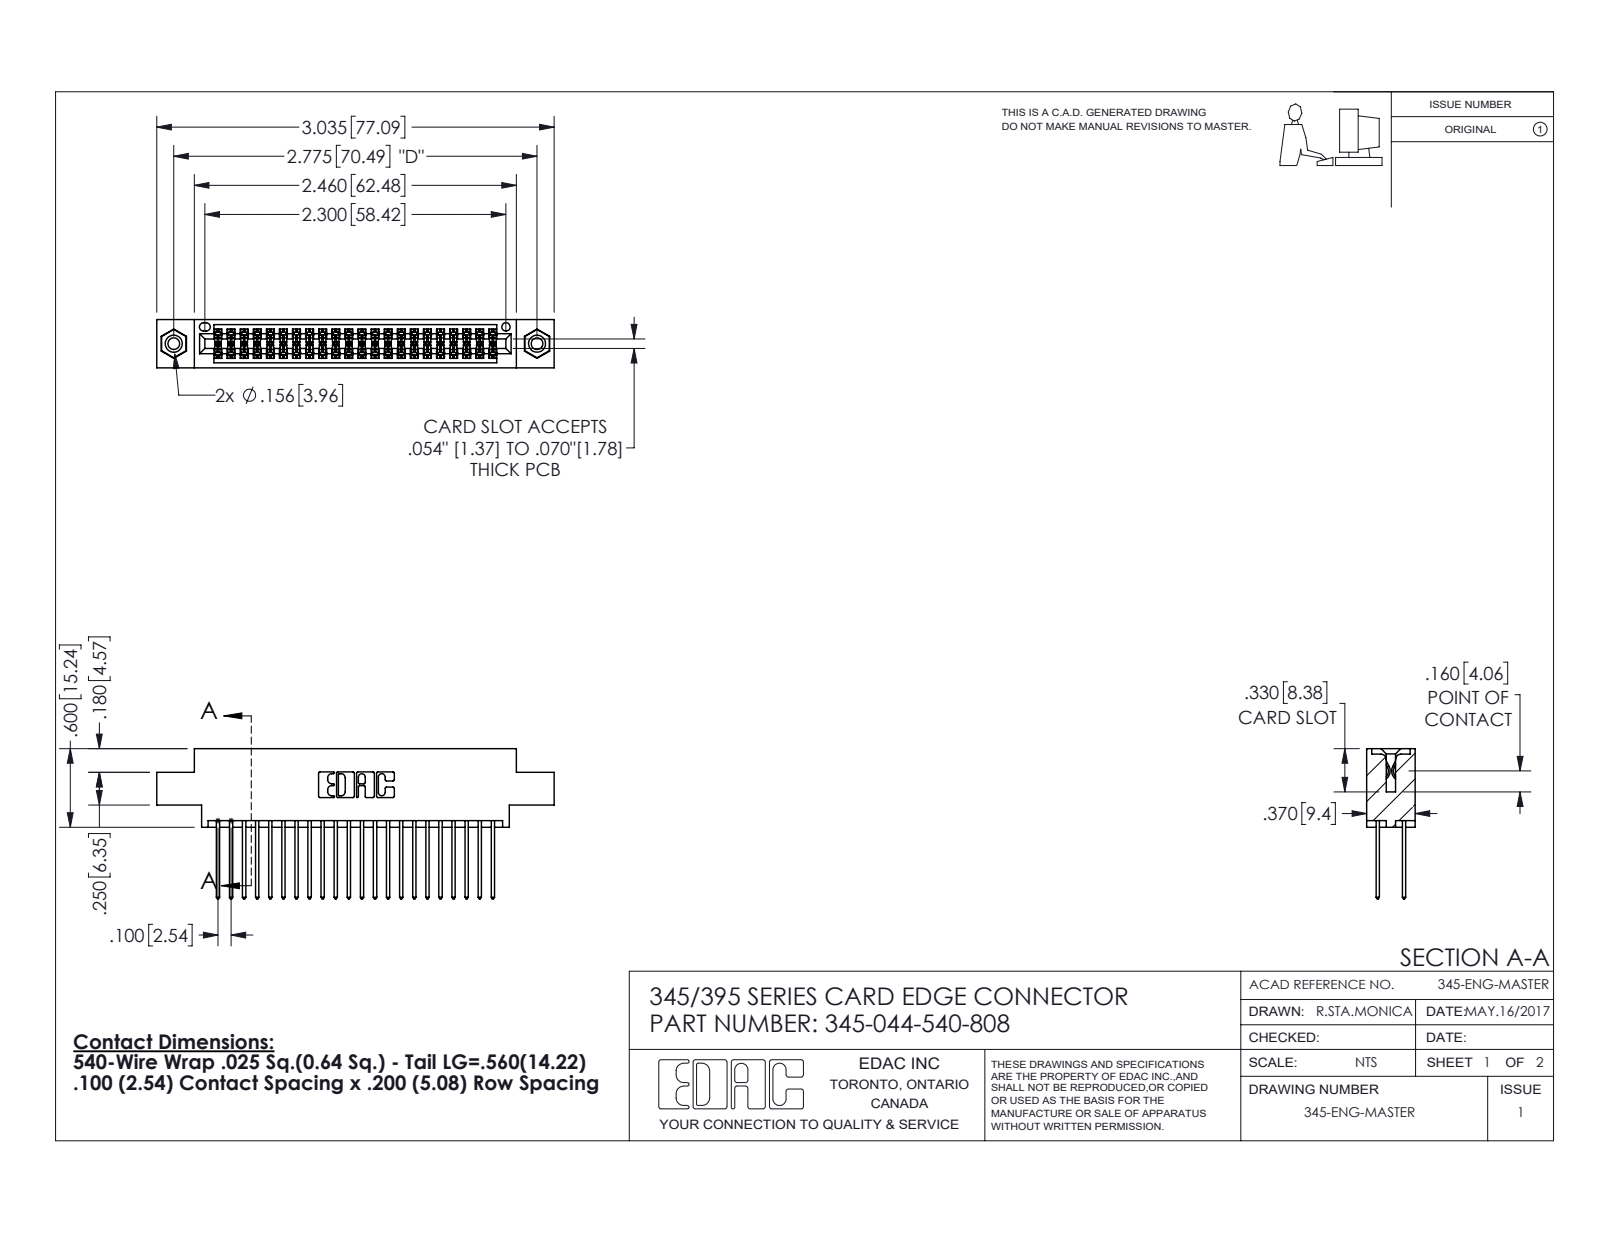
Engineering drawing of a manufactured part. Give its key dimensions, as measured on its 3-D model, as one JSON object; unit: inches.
{"part_name": "345 Part_0.170 Offset - 0.156 Dia-TI; 345-044-540-808; 345-292-001_345-293-140; 345-250-001_345-250-003-102", "step_written_by": "SolidWorks 2016 (CONFIG_CONTROL_DESIGN)", "units": "inches", "bodies": {"solids": 47, "faces": 2390, "planar": 1568, "cylindrical": 806, "other": 16}, "overall_size": [3.035, 1.147, 0.37], "volume_in3": 0.449, "surface_area_in2": 17.68, "round_holes": [[0.089, 2], [0.125, 2], [0.156, 2], [0.064, 1]], "round_bosses_or_shafts": [[0.155, 2]], "partial_cylinders_radius": [[0.006, 66], [0.01, 44], [0.01, 22], [0.007, 6], [0.031, 6], [0.026, 3], [0.014, 2], [0.019, 2]], "face_to_face_distances": [0.072, 0.298, 0.2, 0.098, 0.272, 0.025, 0.37, 0.225, 0.175, 0.149], "hole_center_spacings": [0.27, 2.541, 2.775]}
